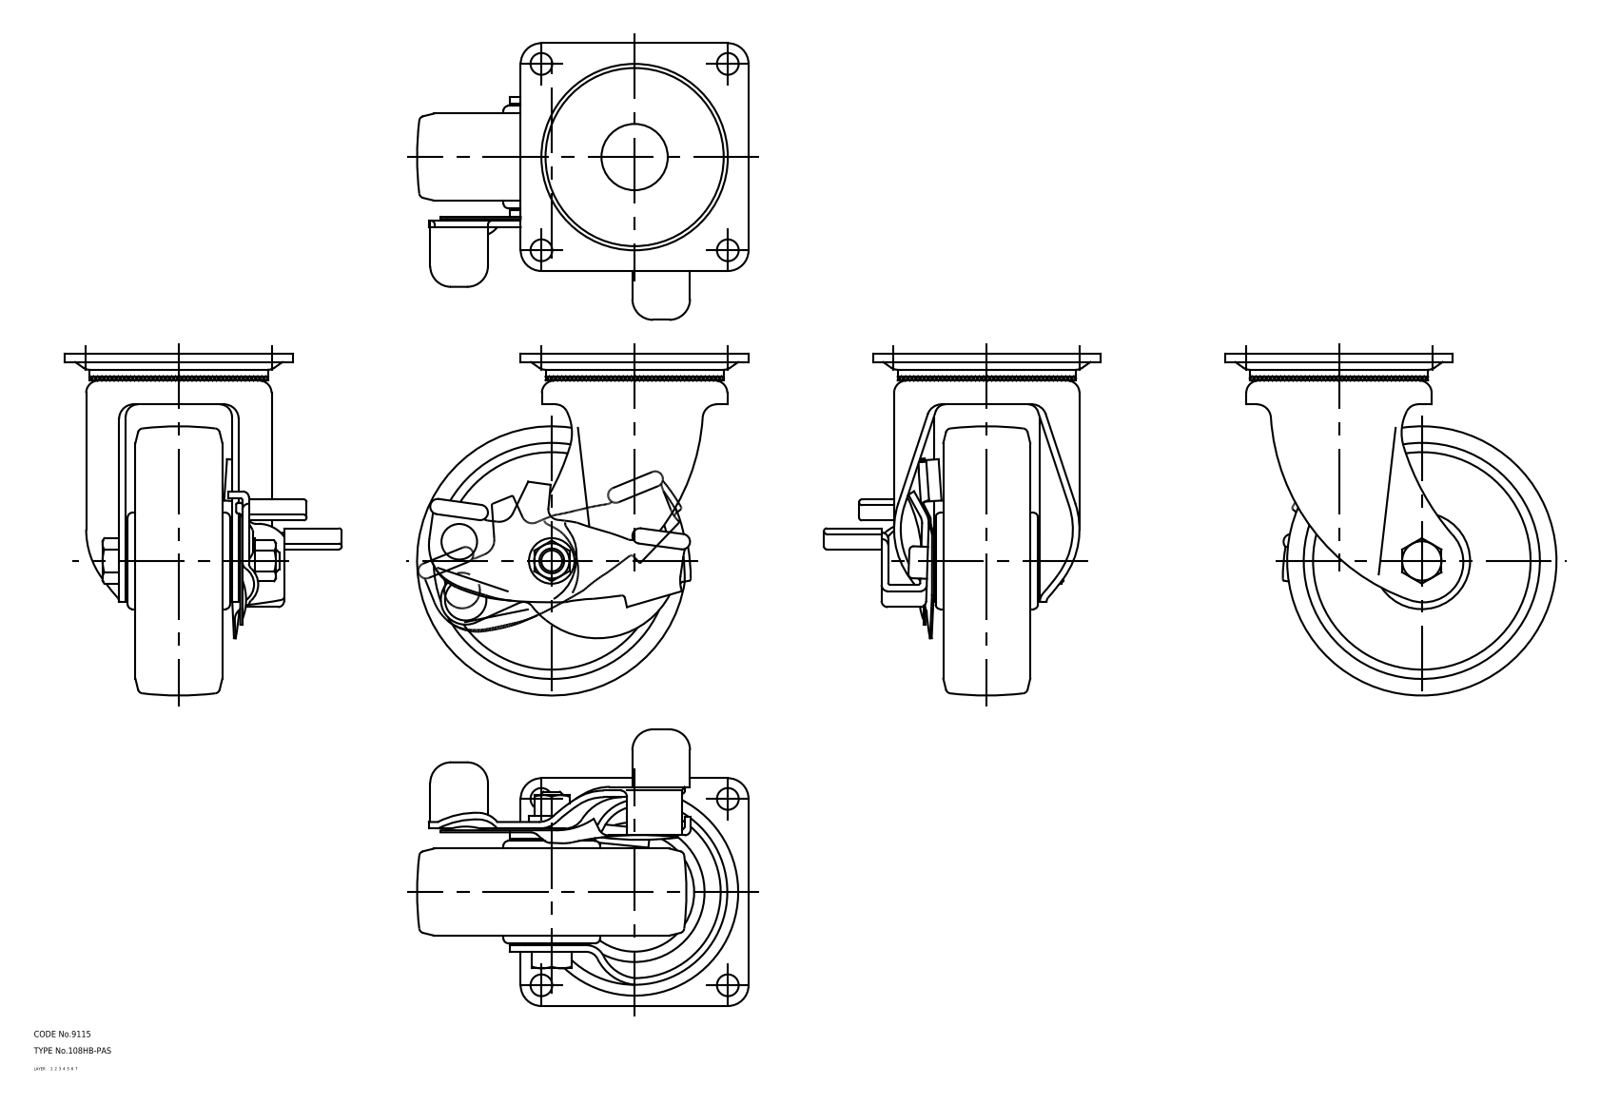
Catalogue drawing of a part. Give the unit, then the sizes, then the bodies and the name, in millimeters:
Units: millimetres
Overall size (bounding box): 165 × 160 × 134.6
Volume: 691 665 mm³ · Surface area: 159 223 mm²
Bodies: 7 solids, 458 faces (0 planar, 0 cylindrical, 458 other)
Part name (STEP PRODUCT): 67139226; 67139239; 67139252; 67139265 (+3 more)
STEP written by: CADfix (AUTOMOTIVE_DESIGN)
